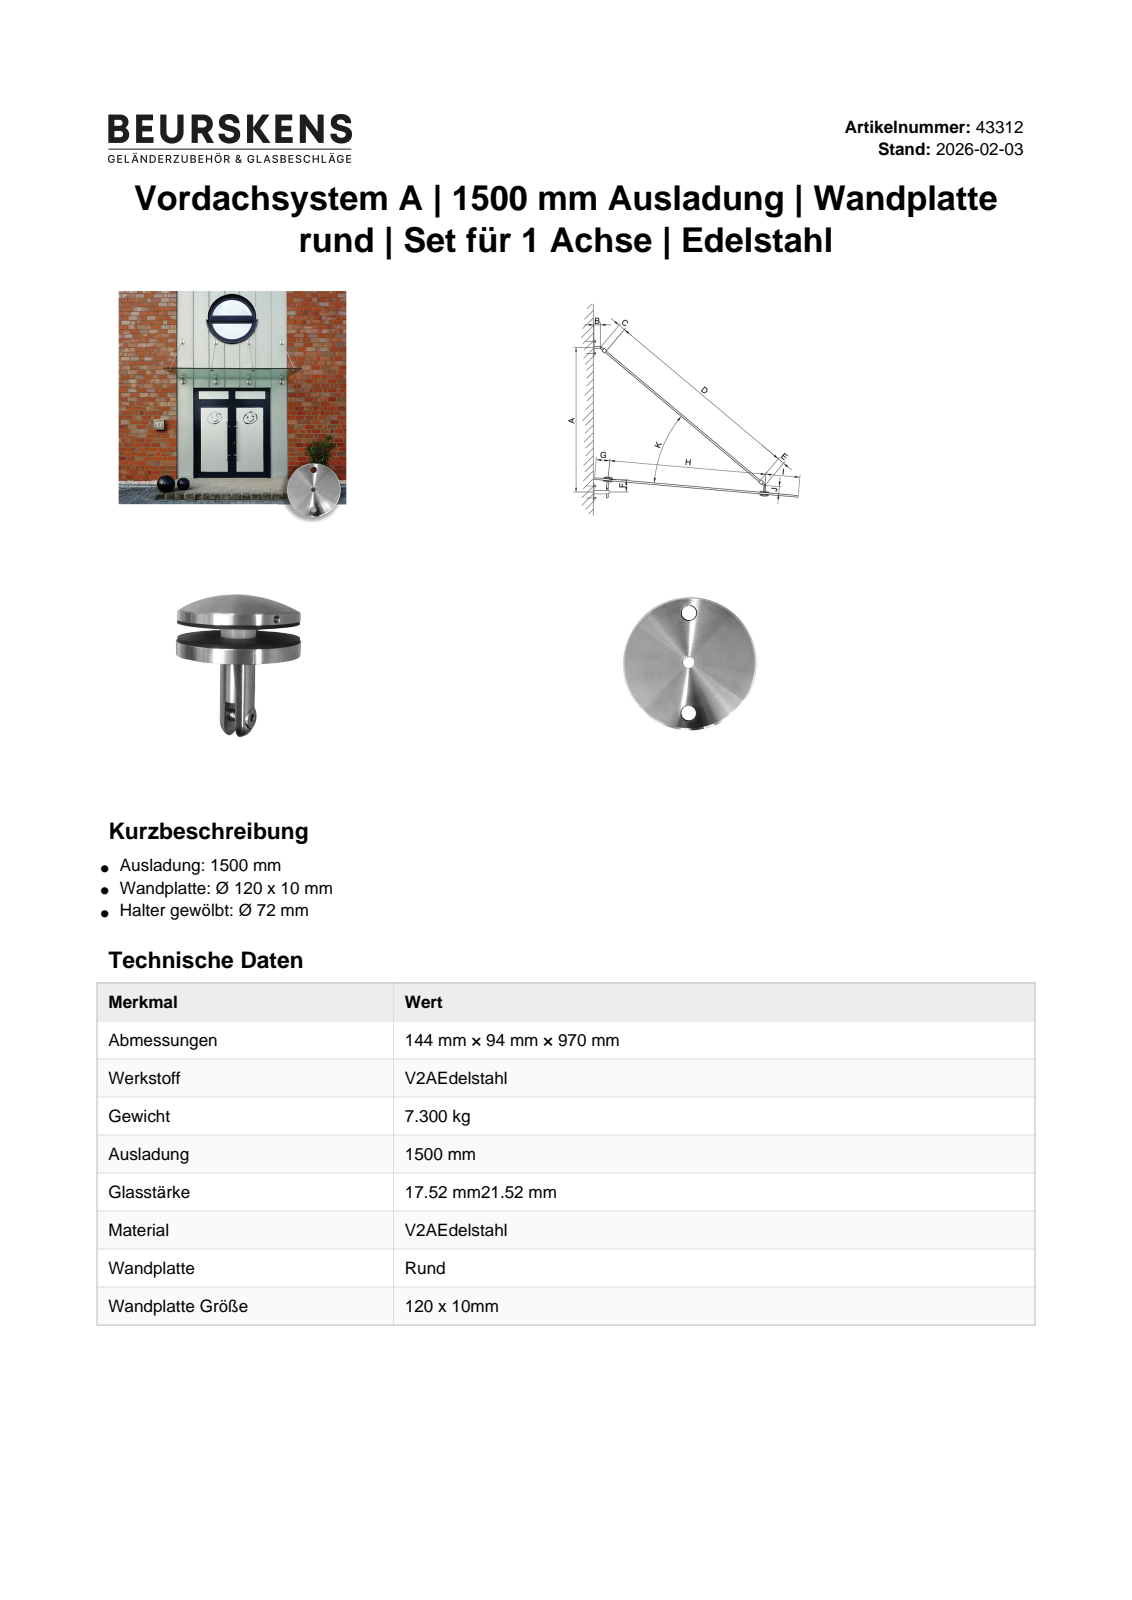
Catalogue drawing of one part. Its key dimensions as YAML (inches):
part_name: "43312; 41122; 41785; DIN 7991 - M10x12 (+8 more)"
step_written_by: "Autodesk Inventor 2022 (AUTOMOTIVE_DESIGN)"
units: inches
bodies: {solids: 31, faces: 311, planar: 169, cylindrical: 96, other: 46}
overall_size: [53.014, 48.031, 4.724]
volume: 51.42
surface_area: 420.8
round_holes:
  - {diameter: 0.394, count: 11}
  - {diameter: 0.197, count: 5}
  - {diameter: 0.413, count: 4}
  - {diameter: 0.512, count: 4}
  - {diameter: 0.551, count: 4}
  - {diameter: 0.559, count: 4}
  - {diameter: 0.315, count: 3}
  - {diameter: 0.335, count: 3}
  - {diameter: 0.492, count: 3}
  - {diameter: 0.118, count: 2}
  - {diameter: 0.709, count: 2}
  - {diameter: 0.827, count: 1}
round_bosses_or_shafts:
  - {diameter: 0.787, count: 7}
  - {diameter: 2.835, count: 4}
  - {diameter: 2.756, count: 4}
  - {diameter: 0.472, count: 3}
  - {diameter: 4.724, count: 2}
  - {diameter: 0.945, count: 2}
  - {diameter: 0.795, count: 2}
  - {diameter: 0.63, count: 2}
face_to_face_distances: [0.394, 1.005, 0.079, 0.926, 1.241, 0.315, 0.315, 1.32, 1.32, 0.394]
hole_center_spacings: [1.772, 43.307, 1.26, 3.543, 41.535, 45.079, 0.012, 0.013]
